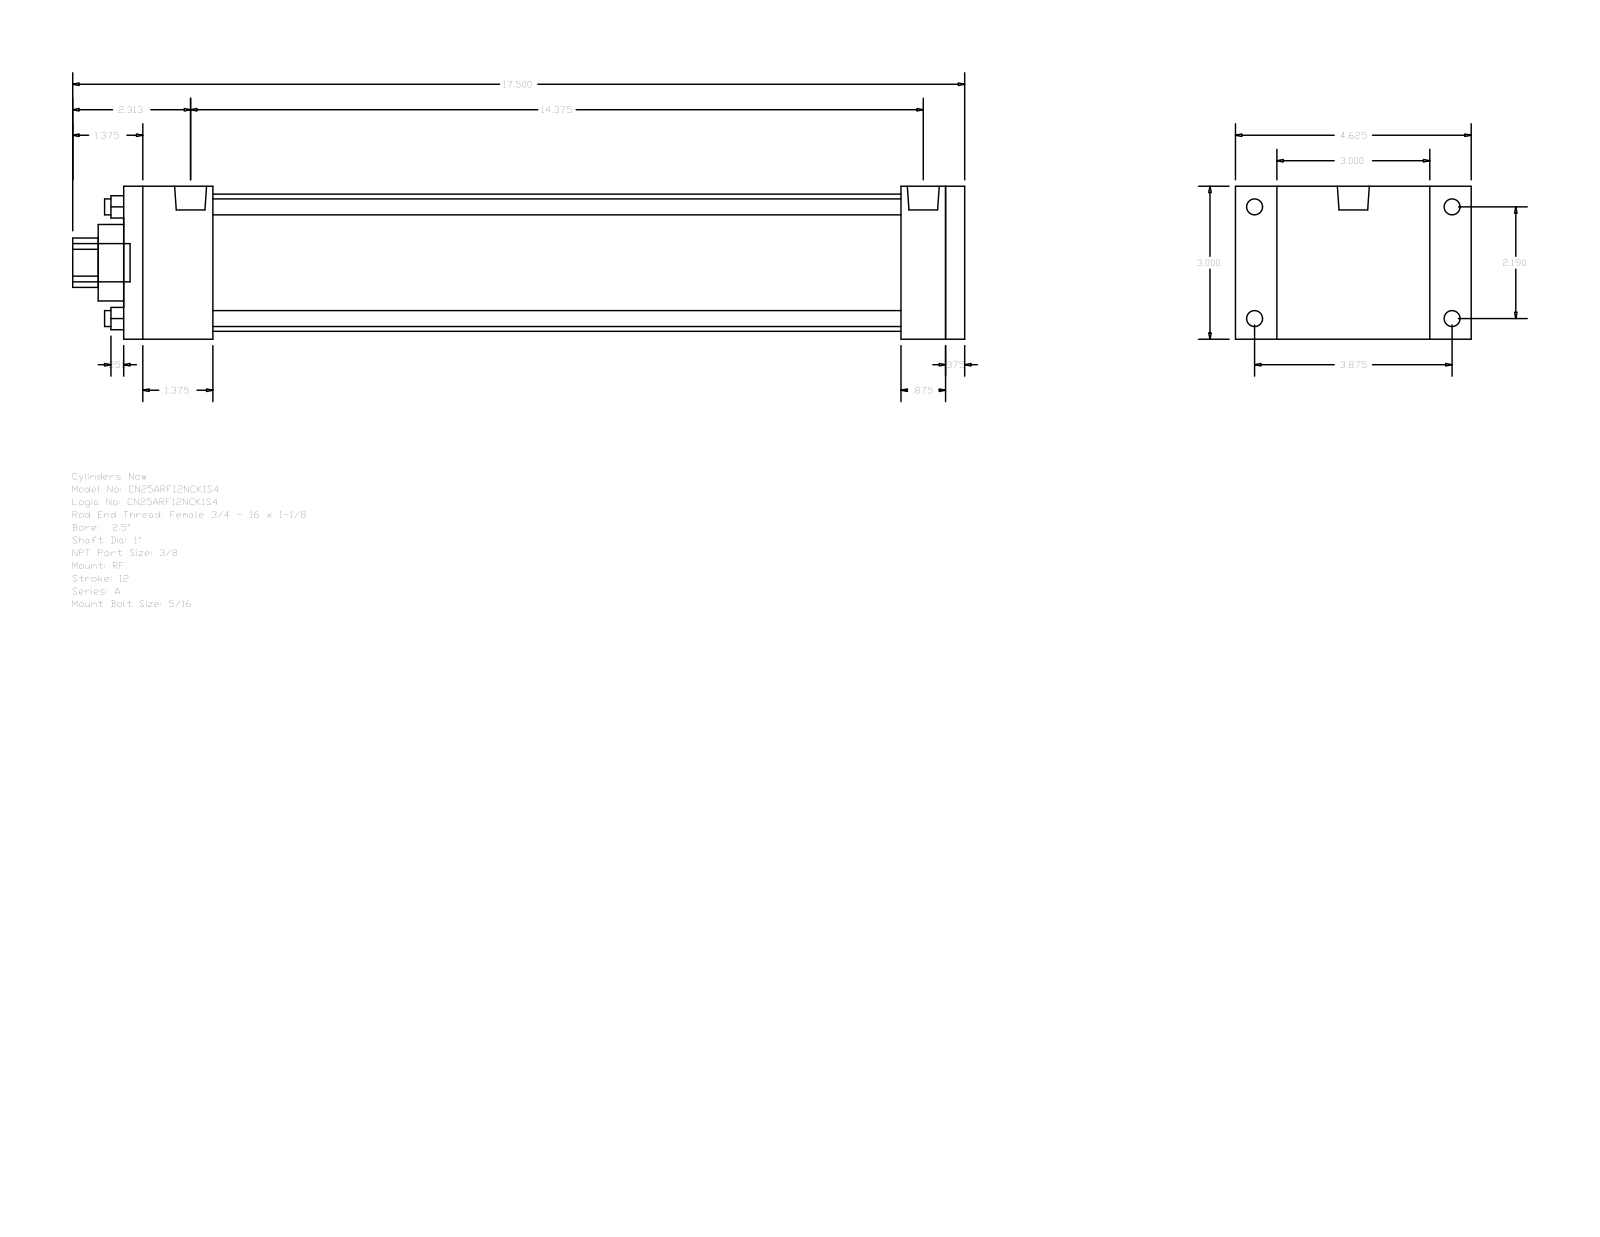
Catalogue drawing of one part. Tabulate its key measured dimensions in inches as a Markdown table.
| quantity | value |
| --- | --- |
| part name | A_RF__0250_1 |
| STEP written by | GSSL Pune (CONFIG_CONTROL_DESIGN) |
| units | inches |
| bodies | 0 solids, 92 faces (64 planar, 28 cylindrical, 0 other) |
| overall size | 17.5 × 4.625 × 3 |
| round holes (diameter × count) | 0.313 × 4, 1 × 1, 1.5 × 1, 2.69 × 1 |
| round bosses / shafts (diameter × count) | 0.313 × 4, 0.219 × 4, 0.627 × 2, 0.75 × 1 |
| partial cylindrical surfaces (radius × count) | 0.484 × 1 |
| main face-to-face distances | 3, 16.5, 0.375, 16.125, 1.75, 15.25, 13.5, 14.375, 14.75, 0.875 |
| hole center spacings | 1.548, 2.19, 3.097 |
